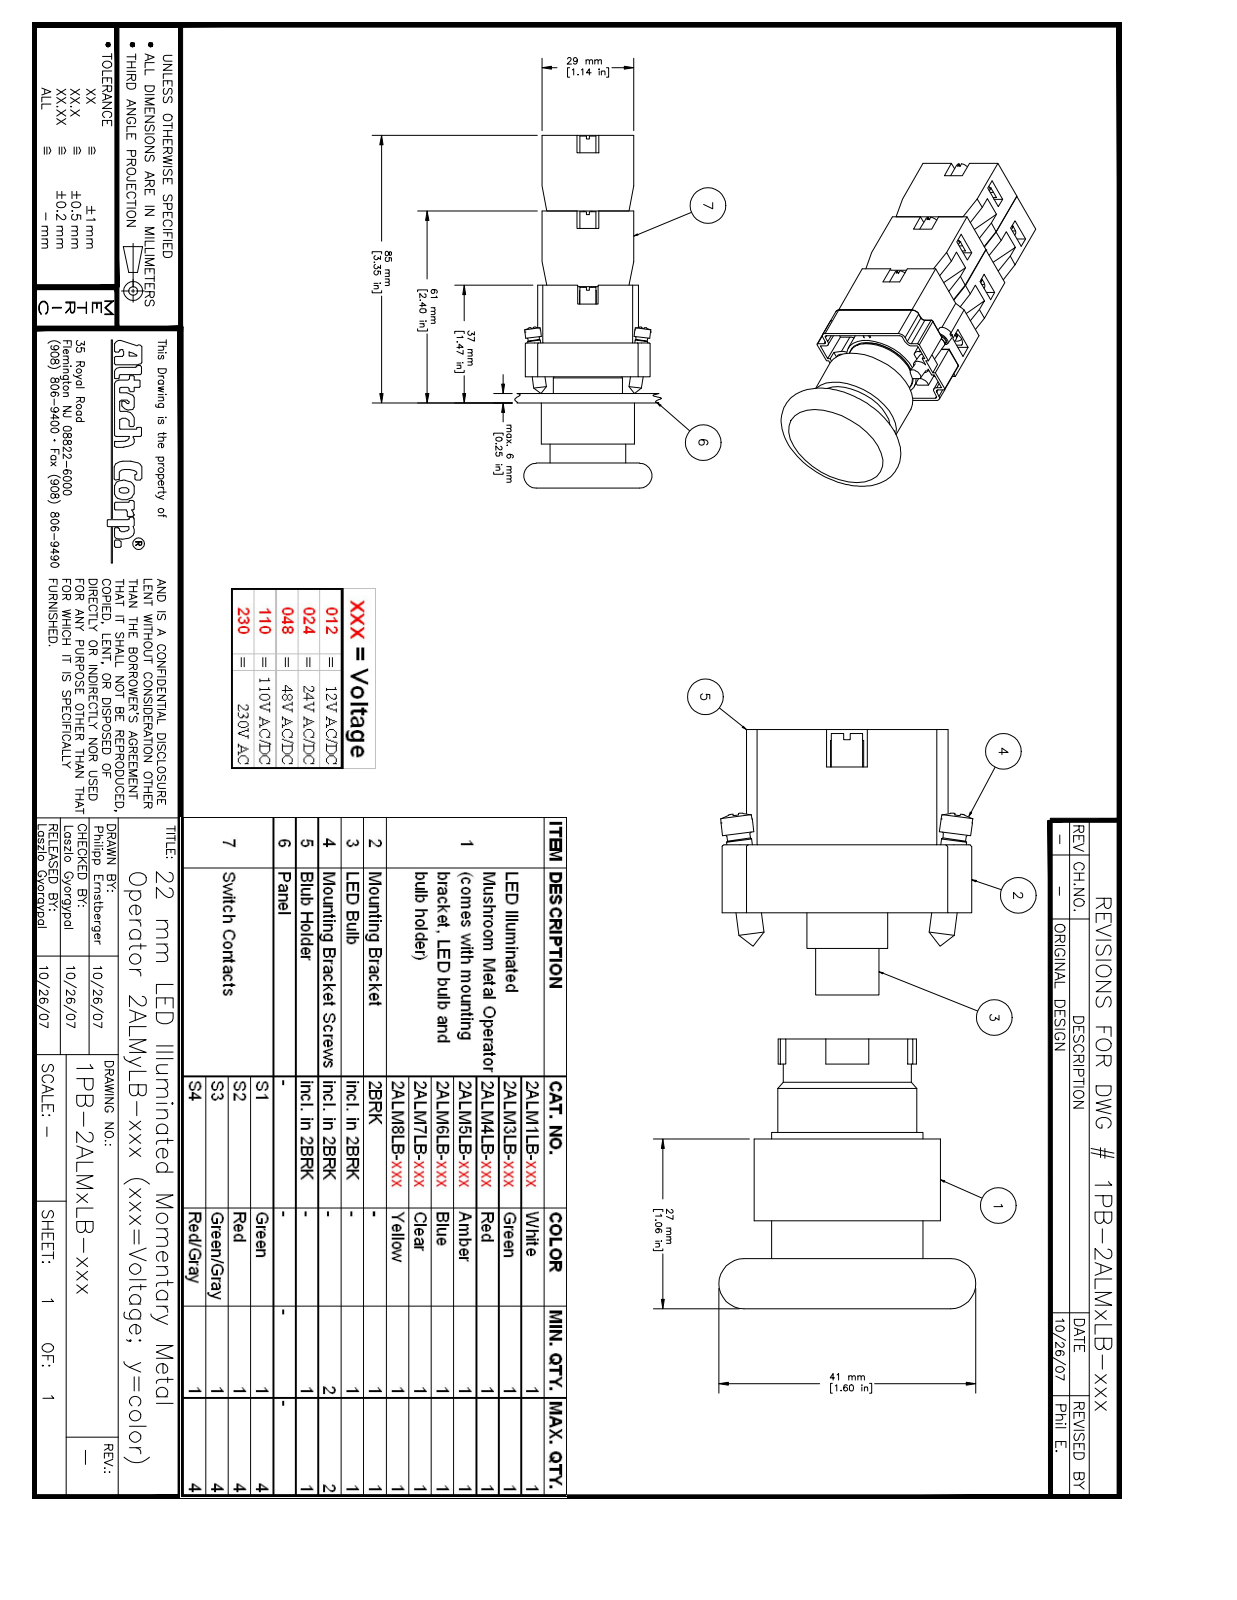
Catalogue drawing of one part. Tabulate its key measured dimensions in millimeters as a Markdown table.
| quantity | value |
| --- | --- |
| part name | 2ALMxLB-xxx_assembly; 2ALMxLB-xxx; rubber_gasket; panel (+8 more) |
| STEP written by | Autodesk Inventor 2008 (AUTOMOTIVE_DESIGN) |
| units | millimeters |
| bodies | 28 solids, 1085 faces (588 planar, 180 cylindrical, 317 other) |
| overall size | 112 × 60.45 × 45 |
| volume | 78 548 mm³ |
| surface area | 50 367 mm² |
| round holes (diameter × count) | 2.5 × 5, 2.6 × 2, 13.5 × 1, 17.75 × 1, 22 × 1, 22.25 × 1, 22.5 × 1, 25.3 × 1, 27.5 × 1, 32.75 × 1 |
| round bosses / shafts (diameter × count) | 3 × 8, 2.75 × 6, 5 × 4, 1.5 × 4, 4 × 2, 3.65 × 2, 29.5 × 1, 24.25 × 1 |
| partial cylindrical surfaces (radius × count) | 1 × 14, 0.25 × 10, 0.72 × 8, 2.25 × 5, 0.5 × 4, 0.8 × 4, 1.8 × 4, 2 × 4 |
| main face-to-face distances | 14.8, 3, 14.7, 24, 19.1, 15.05, 14.95, 29.75, 30, 61 |
| hole center spacings | 14.53, 6.52, 6.57, 13, 25.88, 26, 26.27, 29.07 |
